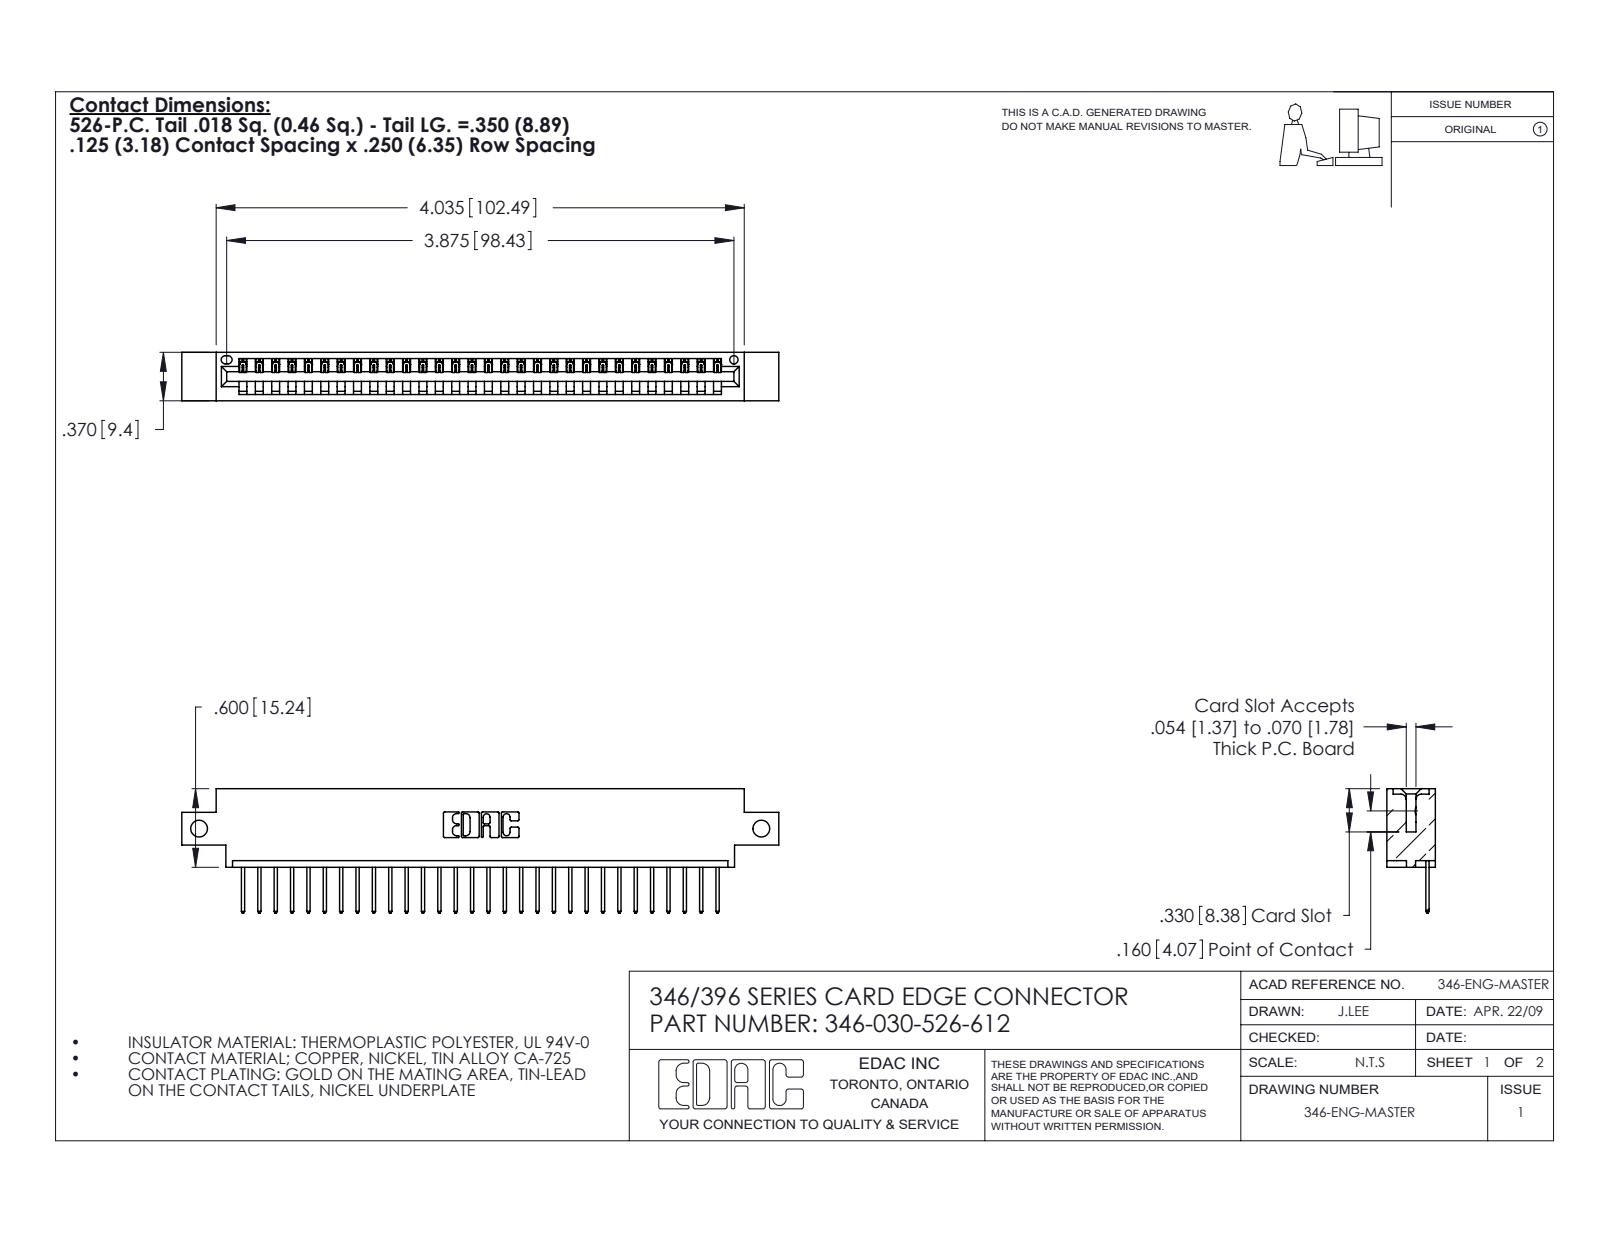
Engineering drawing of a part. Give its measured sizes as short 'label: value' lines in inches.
name: 346 Part_0.170 Offset - Side Mount; 346-030-526-612; 345-292-001_345-293-126
written by: SolidWorks 2020 (CONFIG_CONTROL_DESIGN)
unit: in
bodies: 31 solids, 1866 faces (1280 planar, 586 cylindrical, 0 other)
size: 4.56 × 0.95 × 0.37
volume: 0.655 in³; area: 20.58 in²
holes: 2× ⌀0.128, 1× ⌀0.064
rounds: 60× R0.006, 60× R0.01, 22× R0.01, 6× R0.007, 6× R0.031, 3× R0.026, 2× R0.031, 2× R0.04
face distances: 0.048, 0.322, 0.37, 0.25, 0.072, 0.298, 0.025, 0.148, 0.222, 0.1
hole spacings: 4.295
